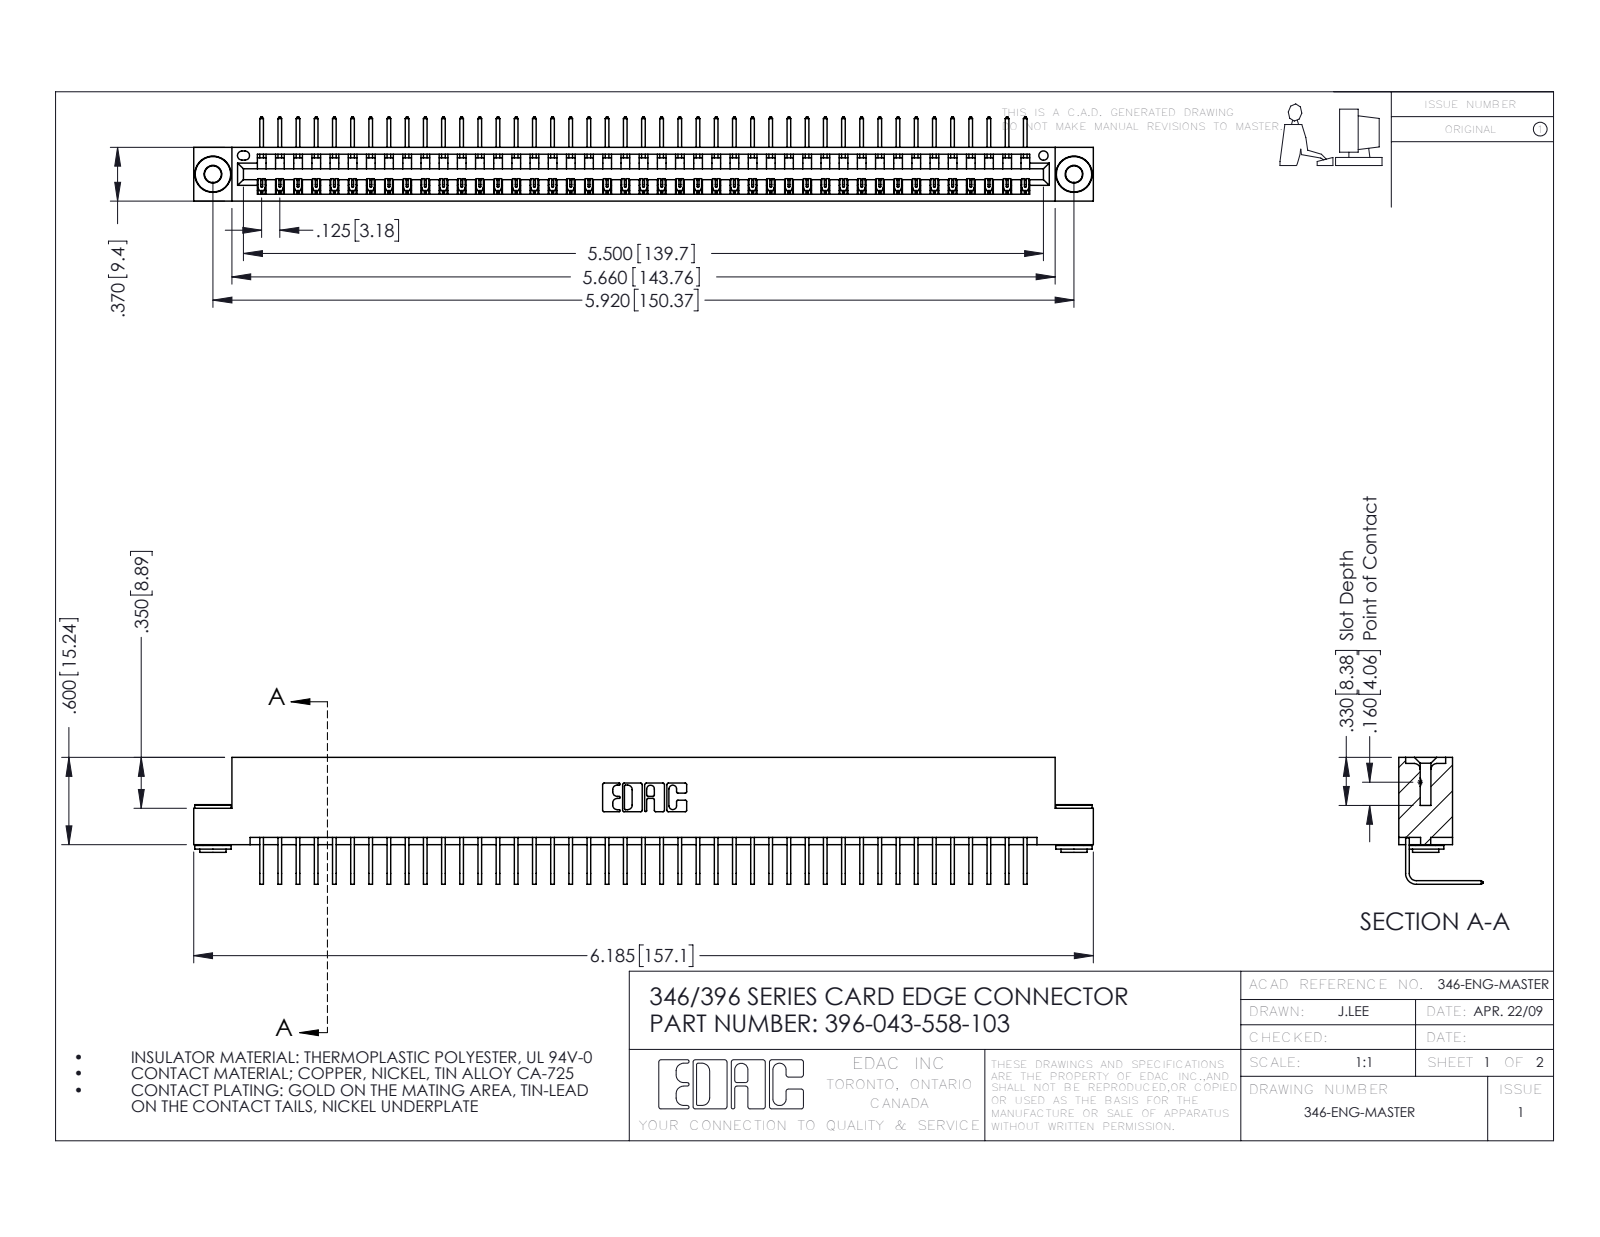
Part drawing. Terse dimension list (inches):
name: 345-292-001_558 Tail - 2; 396-043-558-103; 345-250-002_345-250-002-102; 346 Part_Flush Mounting Lugs - 0.156 Dia-TH
written by: SolidWorks 2016 (CONFIG_CONTROL_DESIGN)
unit: in
bodies: 46 solids, 2740 faces (1892 planar, 840 cylindrical, 8 other)
size: 6.185 × 0.873 × 0.58
volume: 0.928 in³; area: 31.14 in²
holes: 2× ⌀0.116, 2× ⌀0.156, 1× ⌀0.064
bosses: 2× ⌀0.25, 2× ⌀0.18, 2× ⌀0.136
rounds: 86× R0.006, 22× R0.01, 6× R0.007, 6× R0.031, 3× R0.026, 2× R0.031, 2× R0.04, 1× R0.014
face distances: 0.322, 0.048, 0.37, 0.25, 0.025, 0.298, 0.072, 0.148, 0.222, 0.1
hole spacings: 0.246, 5.711, 5.92
